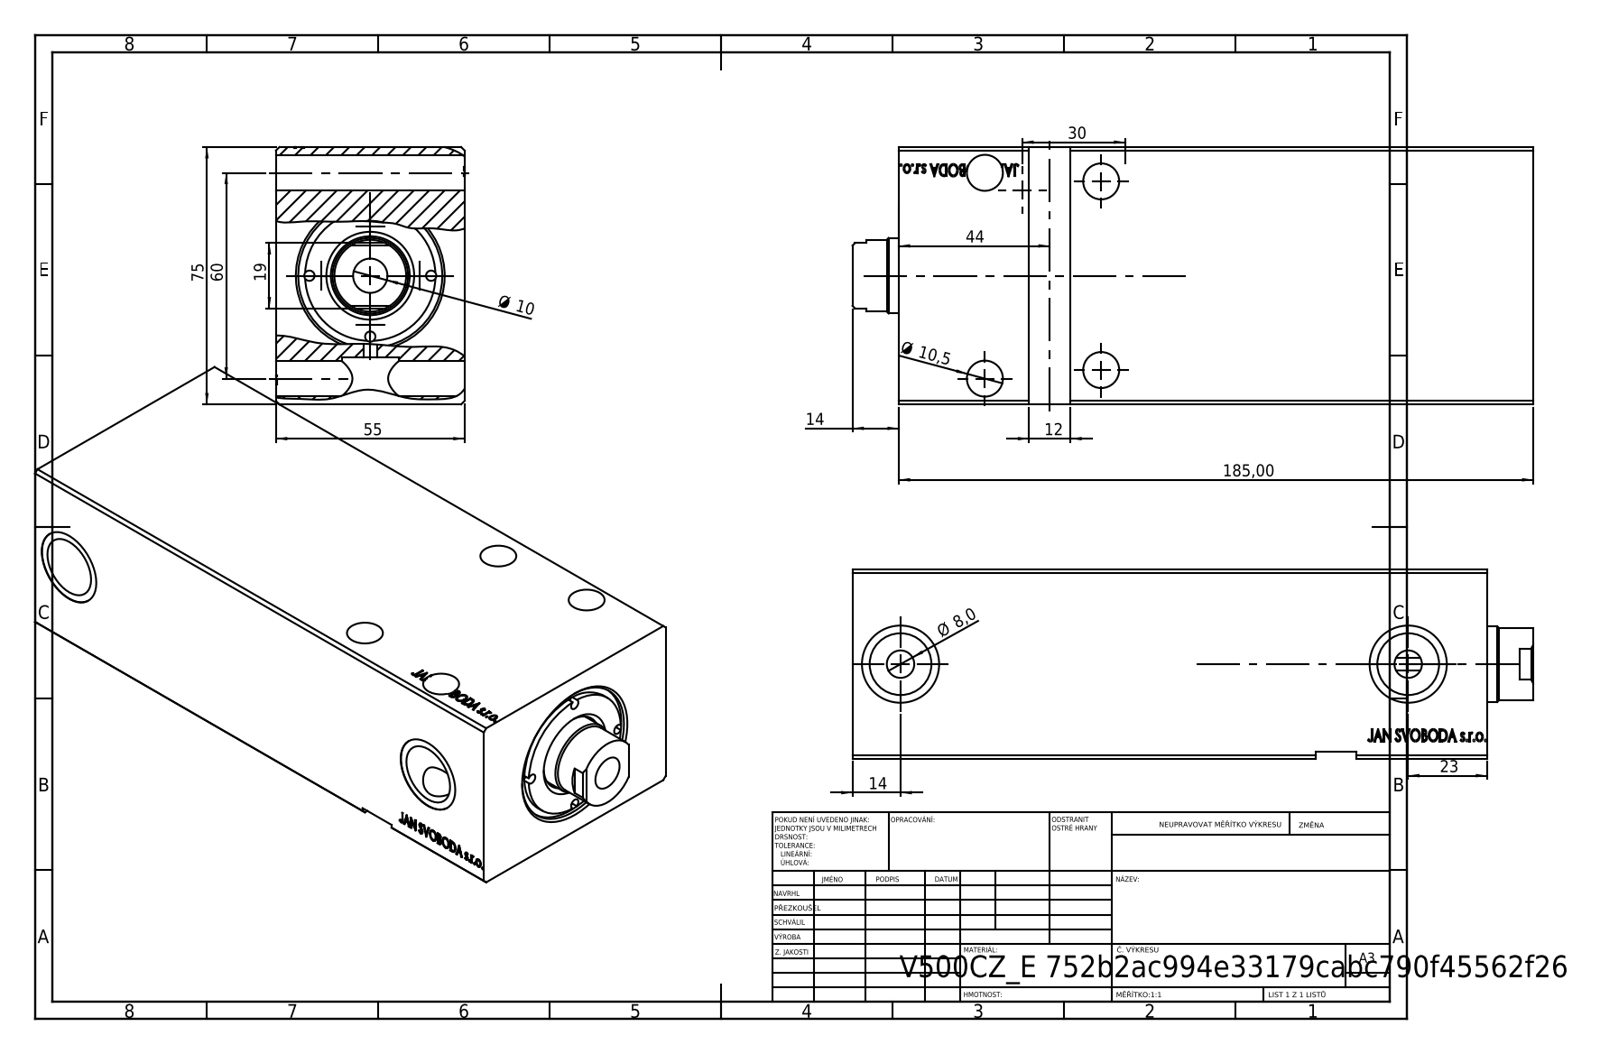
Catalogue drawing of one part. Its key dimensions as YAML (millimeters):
part_name: "V500CZ_E; V500CZ_VCP_E; V500CZ_VC_vysunovaci_E"
step_written_by: "SolidWorks 2019 (CONFIG_CONTROL_DESIGN)"
units: millimeters
bodies: {solids: 3, faces: 782, planar: 376, cylindrical: 54, other: 352}
overall_size: [198.5, 75, 55]
volume: 688601
surface_area: 98952
round_holes:
  - {diameter: 3, count: 4}
  - {diameter: 10.5, count: 4}
  - {diameter: 8, count: 2}
  - {diameter: 18, count: 2}
  - {diameter: 22.5, count: 2}
  - {diameter: 10, count: 1}
  - {diameter: 22, count: 1}
  - {diameter: 23, count: 1}
  - {diameter: 32, count: 1}
  - {diameter: 36, count: 1}
  - {diameter: 42, count: 1}
round_bosses_or_shafts:
  - {diameter: 38, count: 1}
  - {diameter: 20.92, count: 1}
face_to_face_distances: [55, 75, 185, 155, 30, 184.8, 29.8, 11.8, 143.2, 173]
hole_center_spacings: [17.75, 25.1, 34, 35.5, 66.75, 55, 60, 148]
